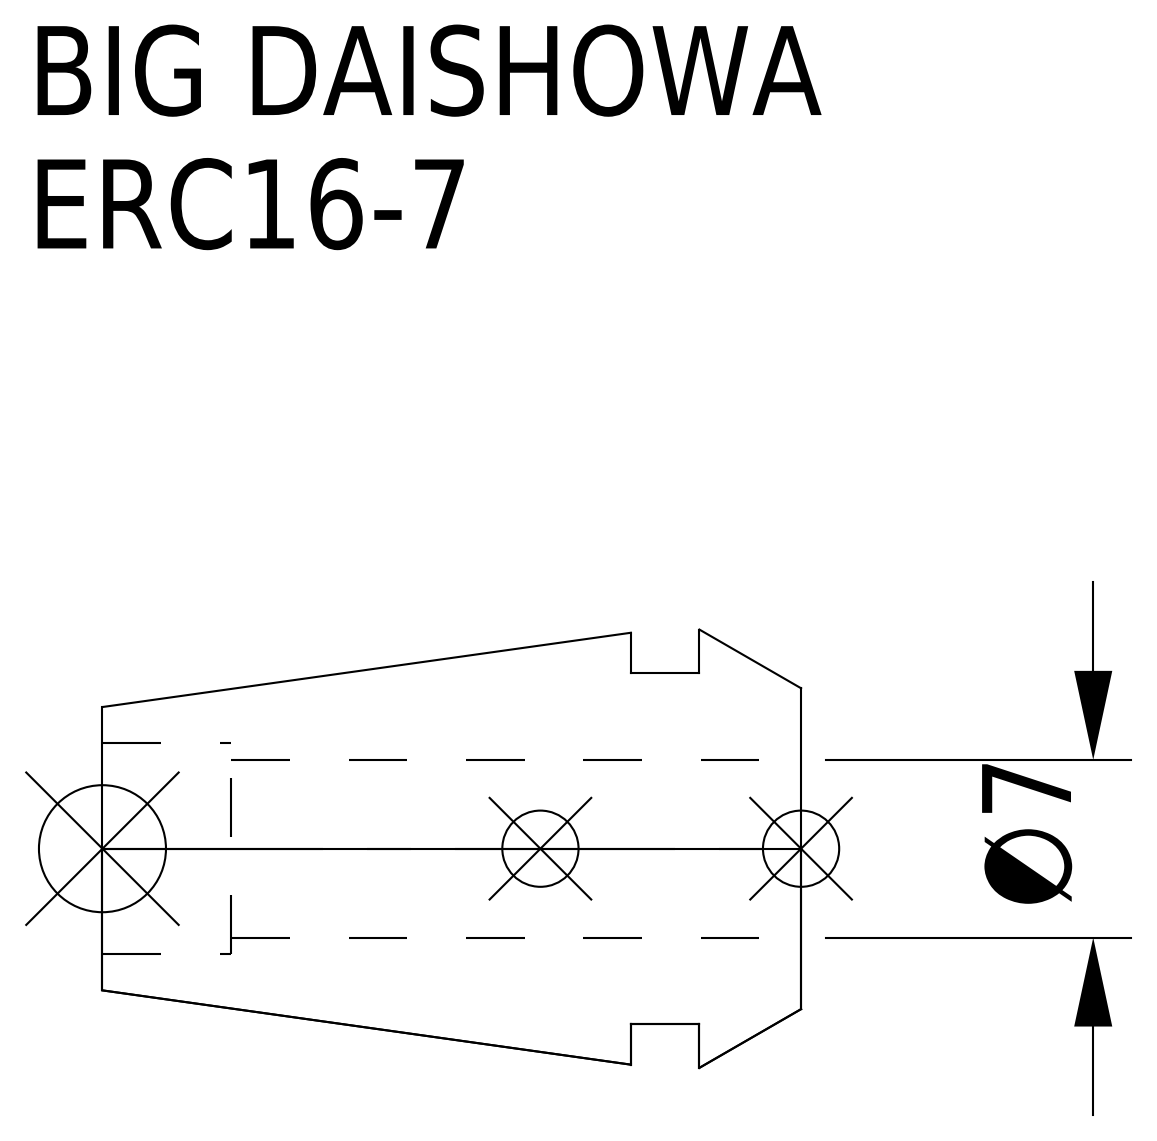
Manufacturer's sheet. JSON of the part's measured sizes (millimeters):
{"part_name": "ERC16-7", "step_written_by": "CREO PARAMETRIC BY PTC INC, 2016380 (AUTOMOTIVE_DESIGN)", "units": "millimeters", "bodies": {"solids": 1, "faces": 15, "planar": 5, "cylindrical": 6, "other": 4}, "overall_size": [27.5, 17.25, 17.25], "volume_mm3": 3257, "surface_area_mm2": 2196, "round_holes": [[7, 1], [8.3, 1]], "round_bosses_or_shafts": [[13.8, 1]], "face_to_face_distances": [4, 6.7, 2.7, 27.5, 23.5, 20.8, 22.43, 18.43, 15.73, 5.07]}
